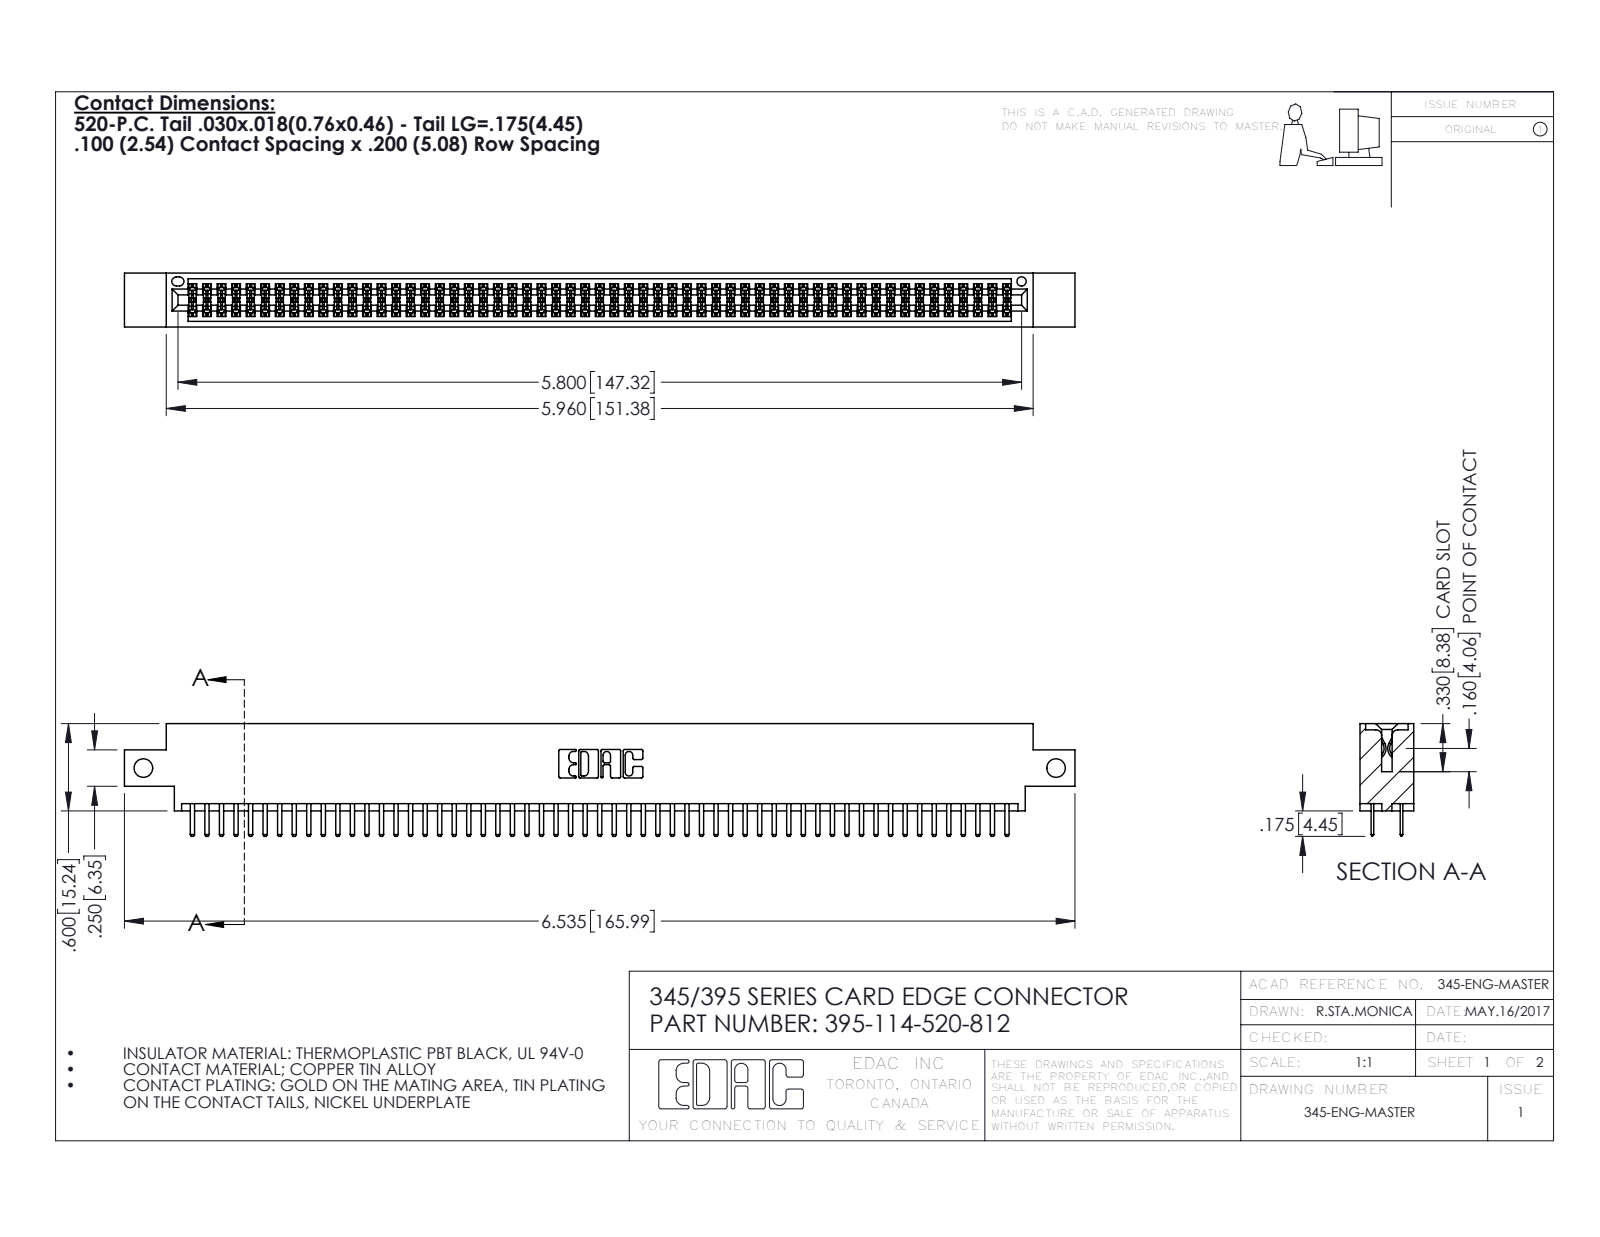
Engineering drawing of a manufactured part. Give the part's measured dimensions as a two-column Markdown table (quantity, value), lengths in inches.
| quantity | value |
| --- | --- |
| part name | 345-292-001_345-293-120; 345 Part_0.170 Offset - Side Mount; 395-114-520-812 |
| STEP written by | SolidWorks 2016 (CONFIG_CONTROL_DESIGN) |
| units | inches |
| bodies | 115 solids, 6286 faces (4074 planar, 2212 cylindrical, 0 other) |
| overall size | 6.535 × 0.775 × 0.37 |
| volume | 0.977 in³ |
| surface area | 36.99 in² |
| round holes (diameter × count) | 0.128 × 2, 0.064 × 1 |
| partial cylindrical surfaces (radius × count) | 0.006 × 171, 0.01 × 118, 0.01 × 22, 0.007 × 6, 0.031 × 6, 0.026 × 3, 0.014 × 2, 0.019 × 2 |
| main face-to-face distances | 0.072, 0.298, 0.2, 0.37, 0.098, 0.272, 0.025, 0.225, 0.022, 0.072 |
| hole center spacings | 6.275 |
